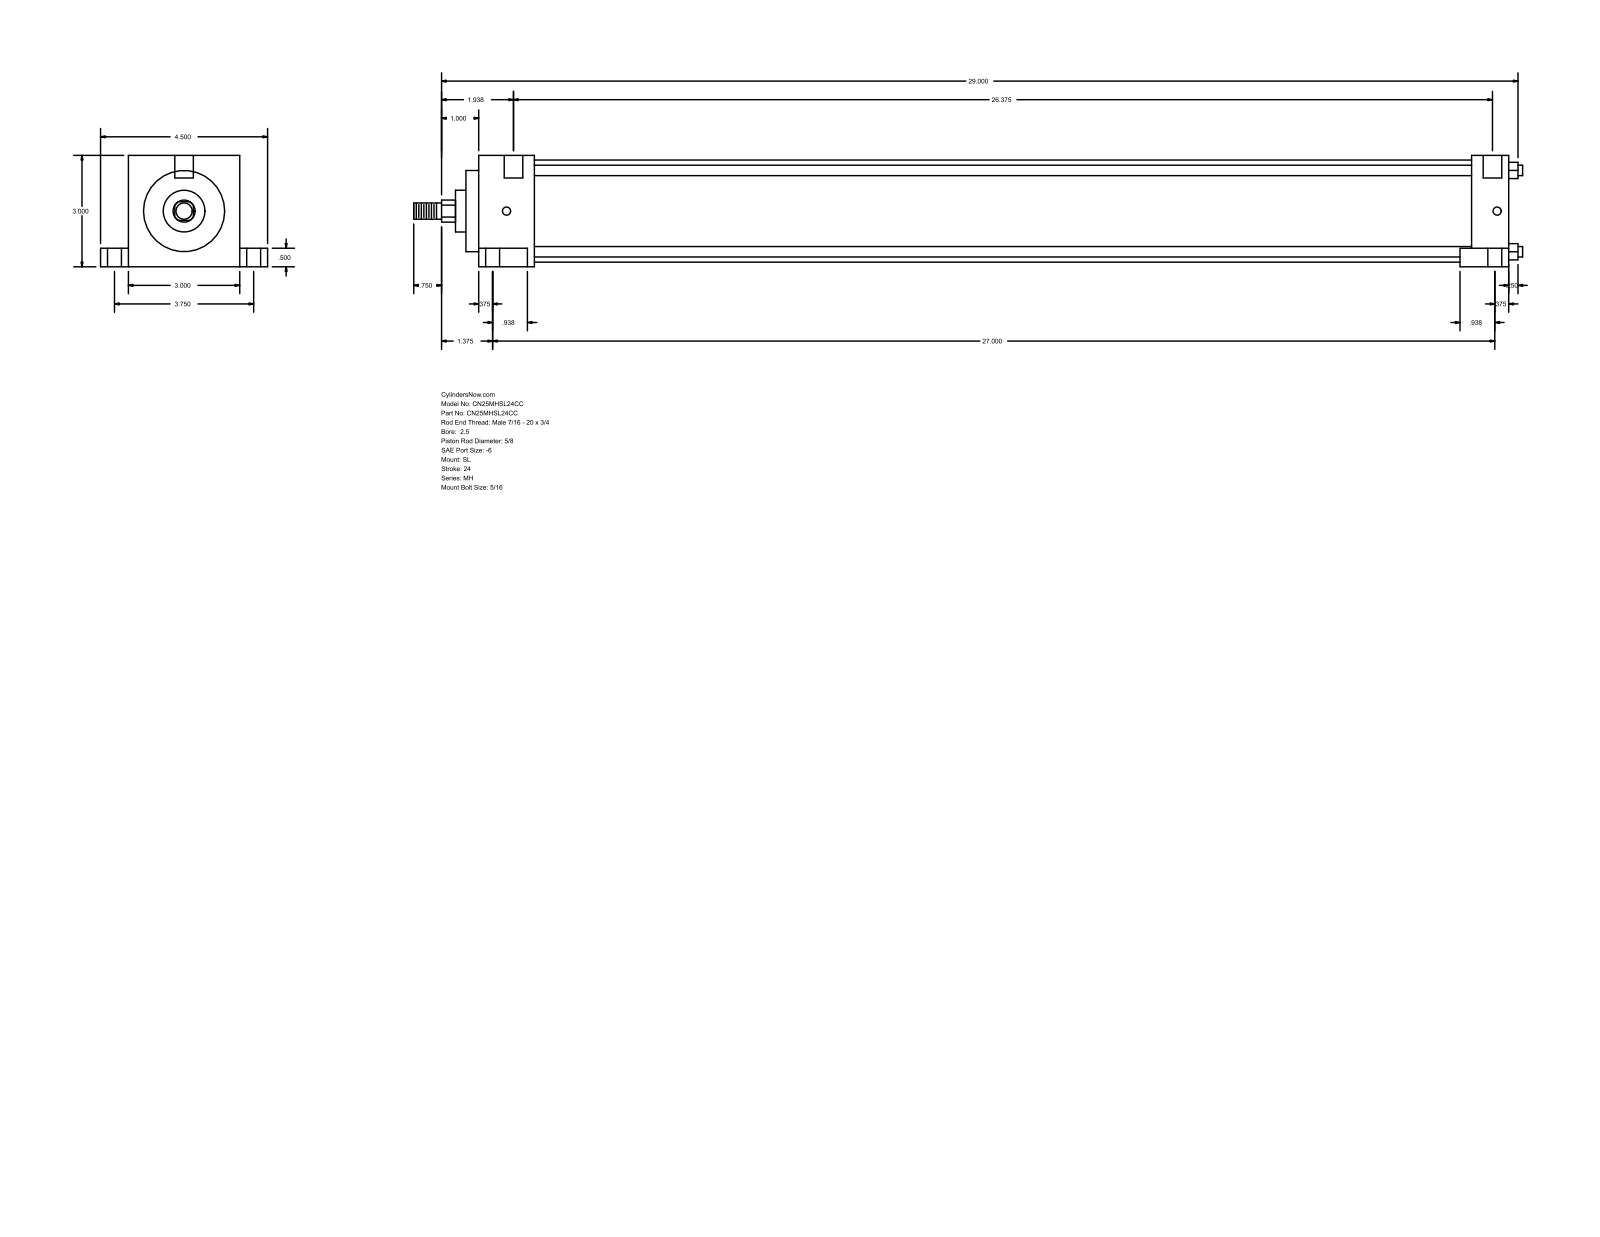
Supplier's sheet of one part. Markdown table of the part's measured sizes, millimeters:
| quantity | value |
| --- | --- |
| part name | MH_SL__0250_0.625 |
| STEP written by | GSSL Pune (CONFIG_CONTROL_DESIGN) |
| units | millimeters |
| bodies | 0 solids, 86 faces (61 planar, 25 cylindrical, 0 other) |
| overall size | 758.83 × 114.3 × 76.2 |
| round holes (diameter × count) | 5.56 × 2, 9.53 × 2, 15.88 × 2, 12.7 × 1 |
| round bosses / shafts (diameter × count) | 7.14 × 4, 69.85 × 1, 55.55 × 1, 28.57 × 1, 15.88 × 1, 11.11 × 1 |
| partial cylindrical surfaces (radius × count) | 7.54 × 1 |
| main face-to-face distances | 76.2, 25.4, 688.18, 713.58, 63.5, 12.7, 19.05, 95.25, 31.75, 680.24 |
| hole center spacings | 47.65, 3.17, 95.24 |
